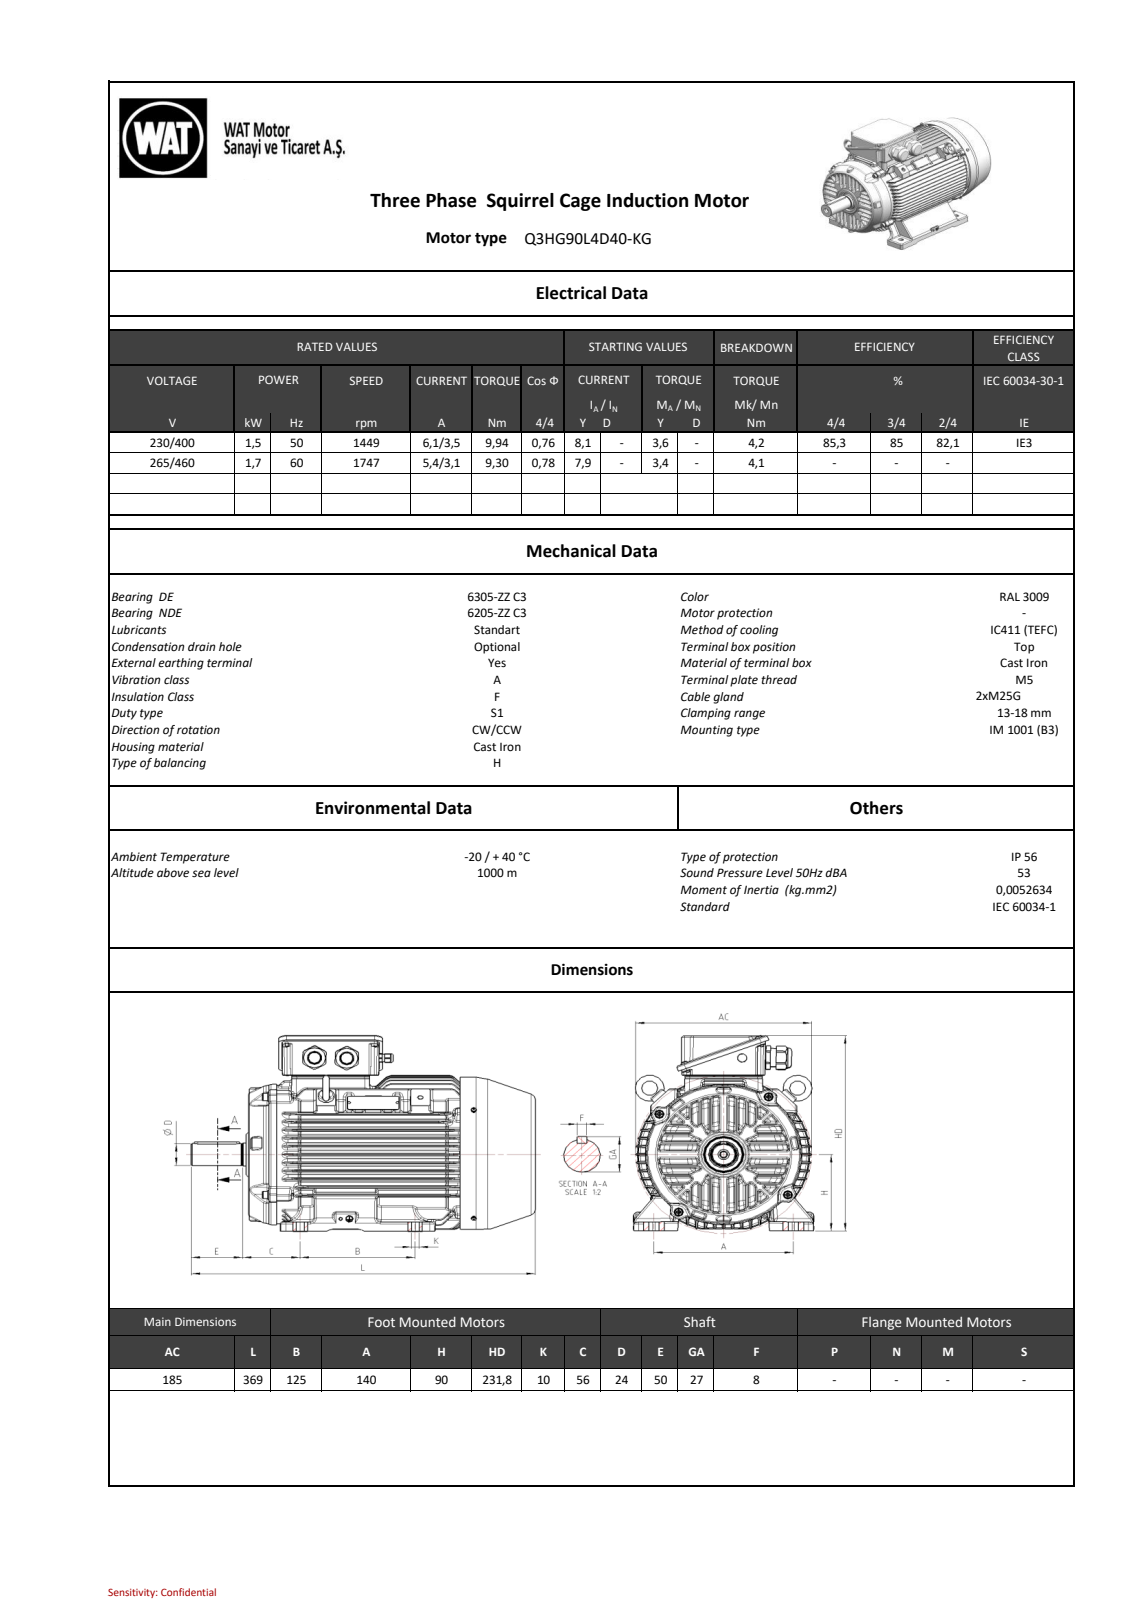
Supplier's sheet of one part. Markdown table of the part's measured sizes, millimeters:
| quantity | value |
| --- | --- |
| part name | C901A24426BAzcyf |
| STEP written by | SIEMENS PLM Software NX 11.0 (AUTOMOTIVE_DESIGN) |
| units | millimeters |
| bodies | 0 solids, 3157 faces (873 planar, 912 cylindrical, 1372 other) |
| overall size | 368.47 × 231.98 × 226.53 |
| round holes (diameter × count) | 10 × 3, 2.5 × 2, 4.2 × 2, 17.2 × 2, 6.5 × 1, 6.8 × 1, 8.4 × 1, 36.9 × 1, 37.1 × 1, 174 × 1 |
| round bosses / shafts (diameter × count) | 20 × 4, 8.65 × 3, 8.5 × 3, 8 × 3, 5 × 3, 27.7 × 2, 25.25 × 2, 176 × 1 |
| partial cylindrical surfaces (radius × count) | 1.5 × 319, 1 × 42, 2 × 41, 4 × 32, 5 × 24, 0.2 × 12, 3 × 12, 26.5 × 12 |
| main face-to-face distances | 12.04, 49.79, 62.58, 3, 3.01, 311.32, 261.53, 1.5, 315.82, 266.03 |
| hole center spacings | 40, 75.01, 112.42 |
